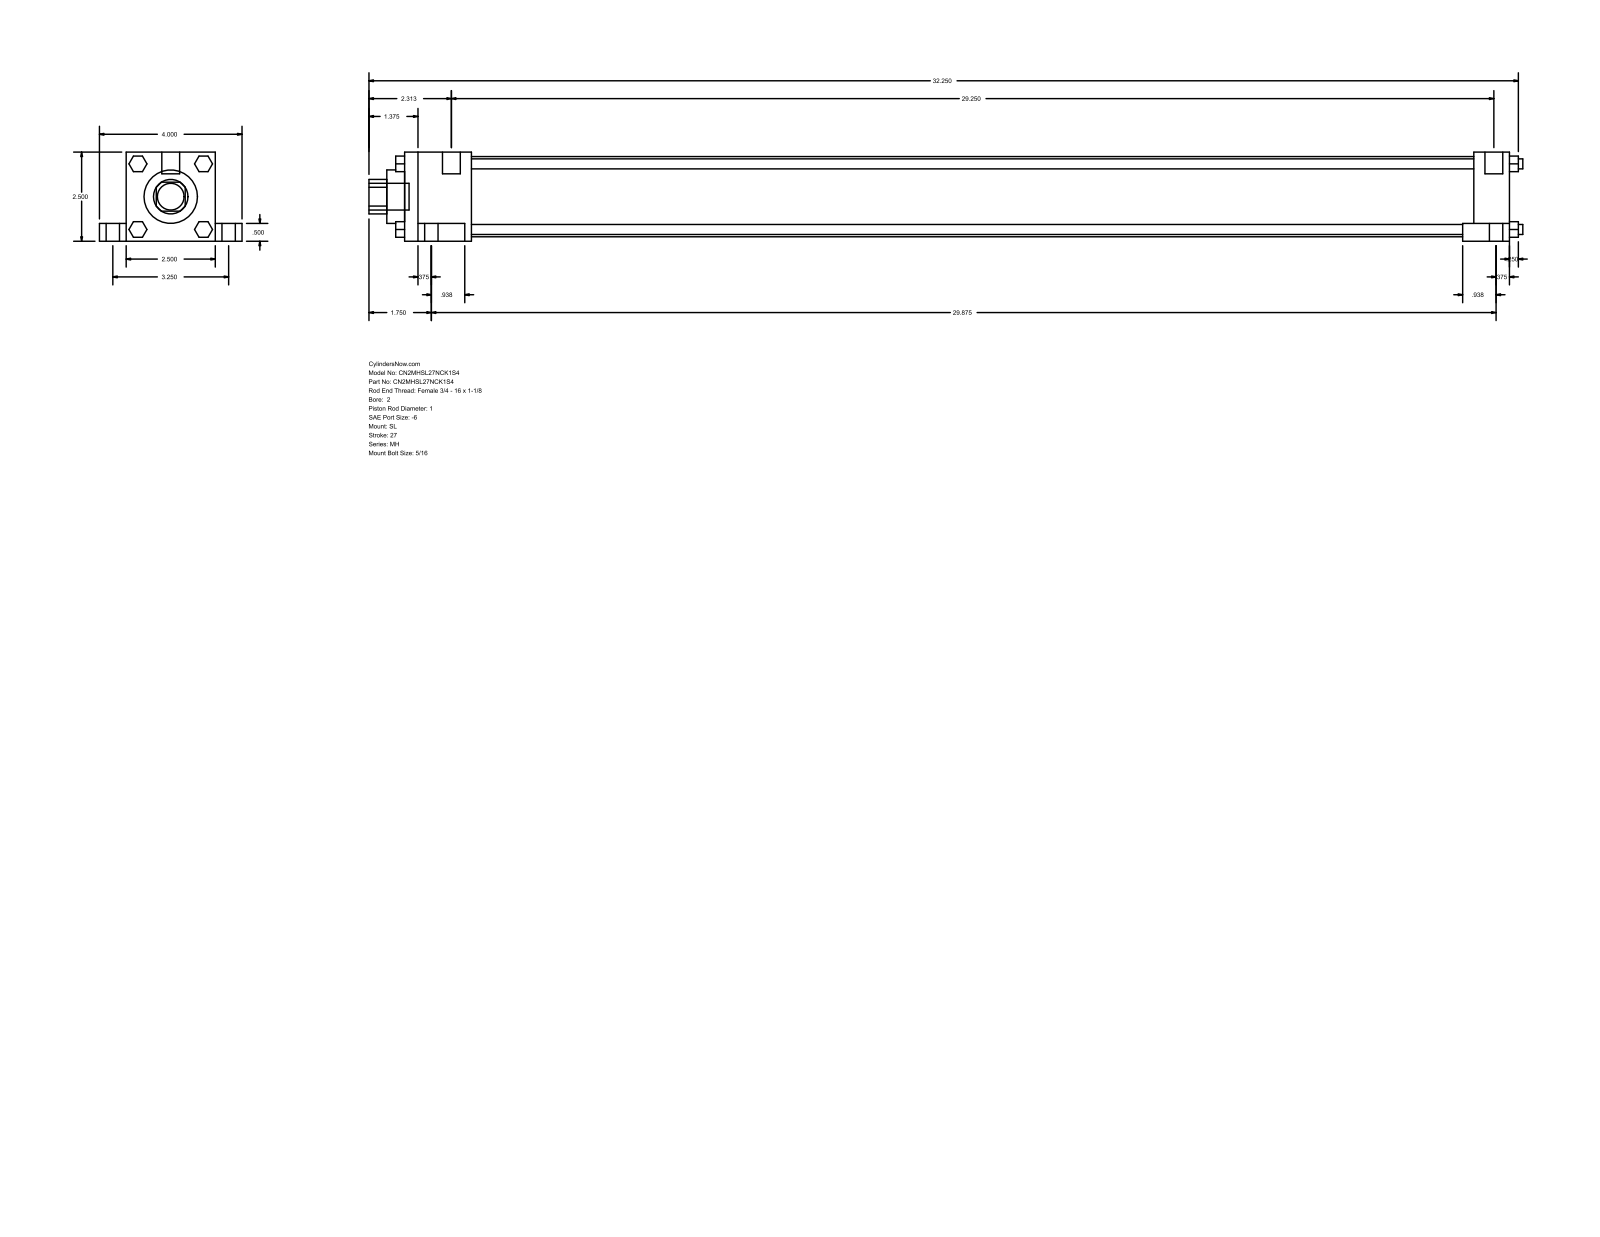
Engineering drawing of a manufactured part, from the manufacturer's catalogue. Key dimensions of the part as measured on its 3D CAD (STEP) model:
Part name (STEP PRODUCT): MH_SL__0200_1
STEP written by: GSSL Pune (CONFIG_CONTROL_DESIGN)
Units: millimetres
Bodies: 0 solids, 148 faces (112 planar, 36 cylindrical, 0 other)
Overall size (bounding box): 822.33 × 101.6 × 63.5
Round holes (diameter × count): ⌀25.4 ×1, ⌀38.1 ×1, ⌀57.15 ×1
Round bosses / shafts (diameter × count): ⌀15.88 ×4, ⌀9.53 ×4, ⌀7.14 ×4, ⌀5.56 ×4, ⌀12.7 ×2, ⌀19.05 ×1
Partial cylindrical surfaces — rounded edges, fillets, slot ends (radius × count): R12.29 ×1
Main face-to-face distances: 63.5, 787.4, 12.7, 19.05, 50.8, 82.55, 25.4, 9.52, 762, 47.63
